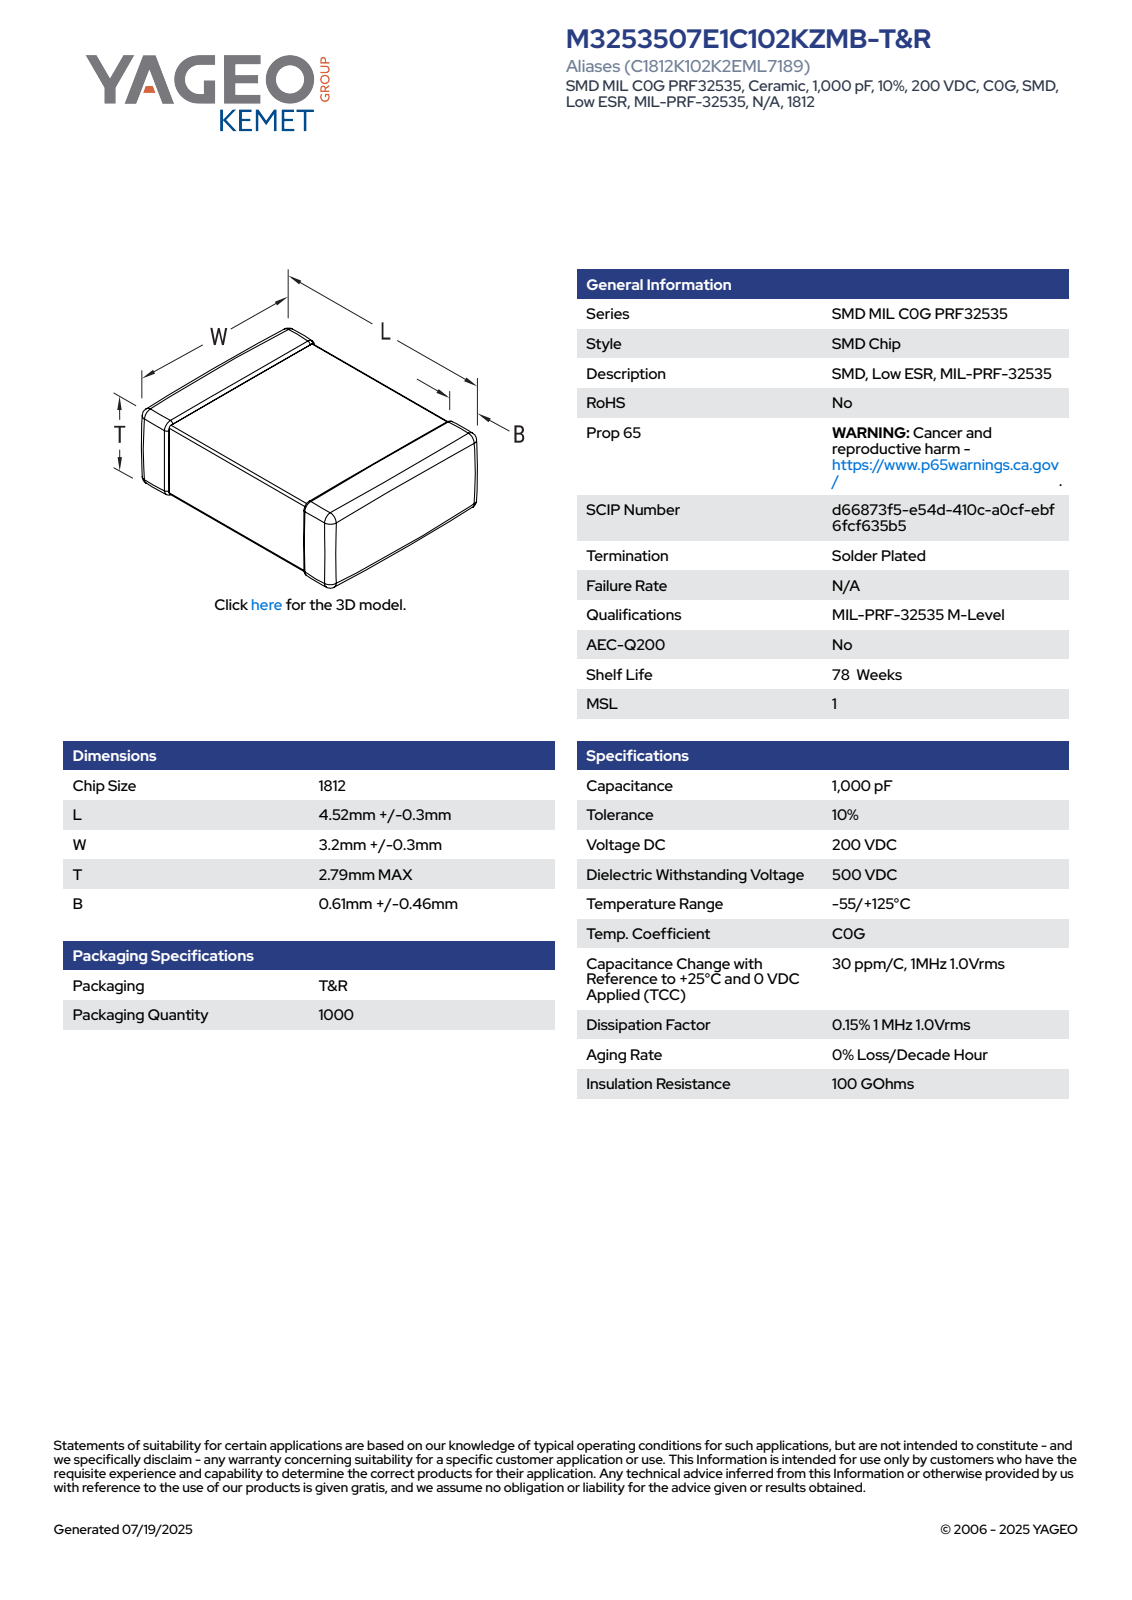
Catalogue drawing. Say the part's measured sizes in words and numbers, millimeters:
The part is named "CCS_STDNOS_1812_L4.82W3.5T2.79B0.61". Its 3-D file was written by "SolidWorks 2014 (AUTOMOTIVE_DESIGN)". It is 4 solids with 125 faces: 71 planar, 38 cylindrical and 16 other. Overall it measures 4.82 by 3.5 by 2.79 millimeters. Its volume is 44 cubic millimeters and its surface area 79 square millimeters. The main face-to-face distances are 2.65, 3.36, 4.82, 2.72, 3.43, 2.79, 3.5, 0.48, 1.94, 1.46.
